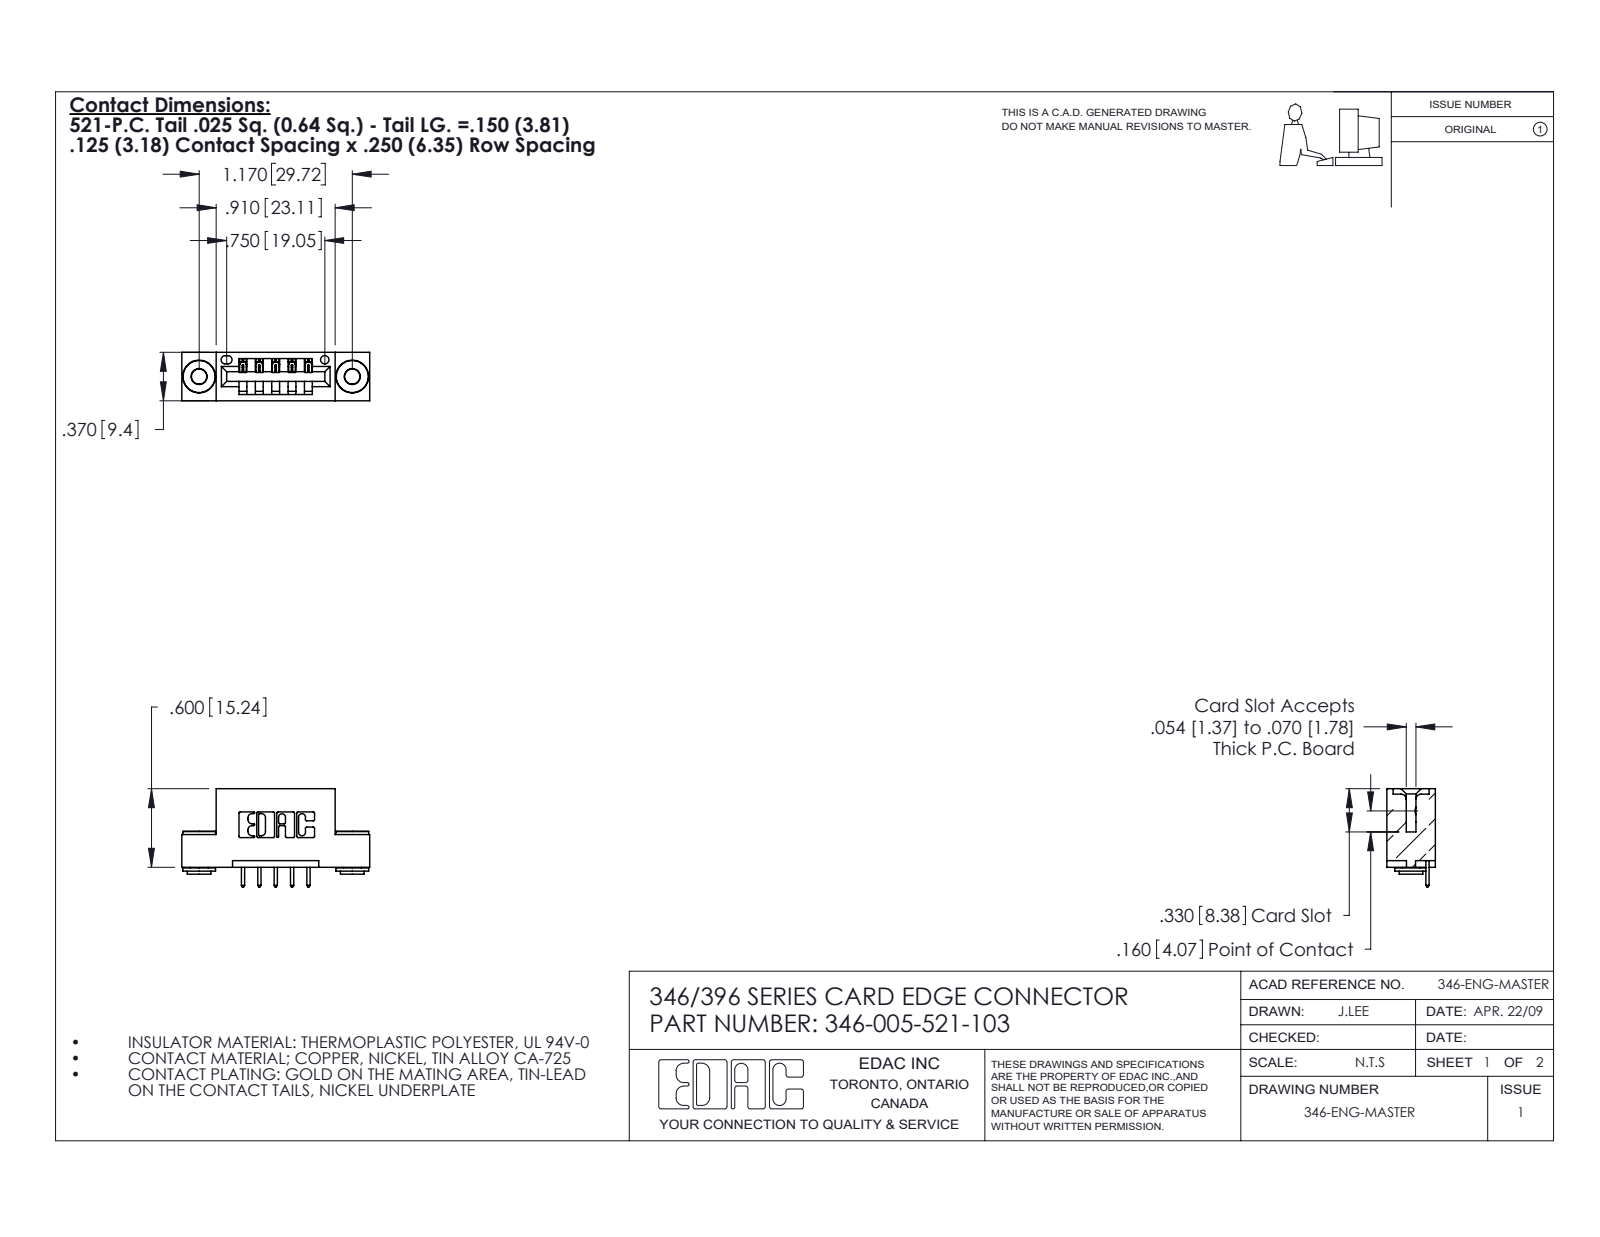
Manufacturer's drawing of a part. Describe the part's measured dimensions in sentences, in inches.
The part is named "346-005-521-103; 345-292-001_345-293-121; 345-250-002_345-250-002-102; 346 Part_Flush Mounting Lugs - 0.156 Dia-TH". Its 3-D file was written by "SolidWorks 2020 (CONFIG_CONTROL_DESIGN)". It is 8 solids with 464 faces: 300 planar, 156 cylindrical and 8 other. Overall it measures 1.435 by 0.75 by 0.37 inches. Its volume is 0.197 cubic inches and its surface area 5.923 square inches. Round holes: 2 of diameter 0.116, 2 of diameter 0.156, 1 of diameter 0.064. Round bosses or shafts: 2 of diameter 0.25, 2 of diameter 0.18, 2 of diameter 0.136. Partial cylindrical surfaces (rounded edges, fillets, slot ends): 22 of radius 0.01, 10 of radius 0.006, 10 of radius 0.01, 6 of radius 0.007, 6 of radius 0.031, 3 of radius 0.026, 2 of radius 0.031, 2 of radius 0.04. The main face-to-face distances are 0.25, 0.37, 0.048, 0.322, 0.148, 0.222, 0.1, 0.174, 0.025, 0.55. The hole center spacings are 0.246, 0.969, 1.17.
